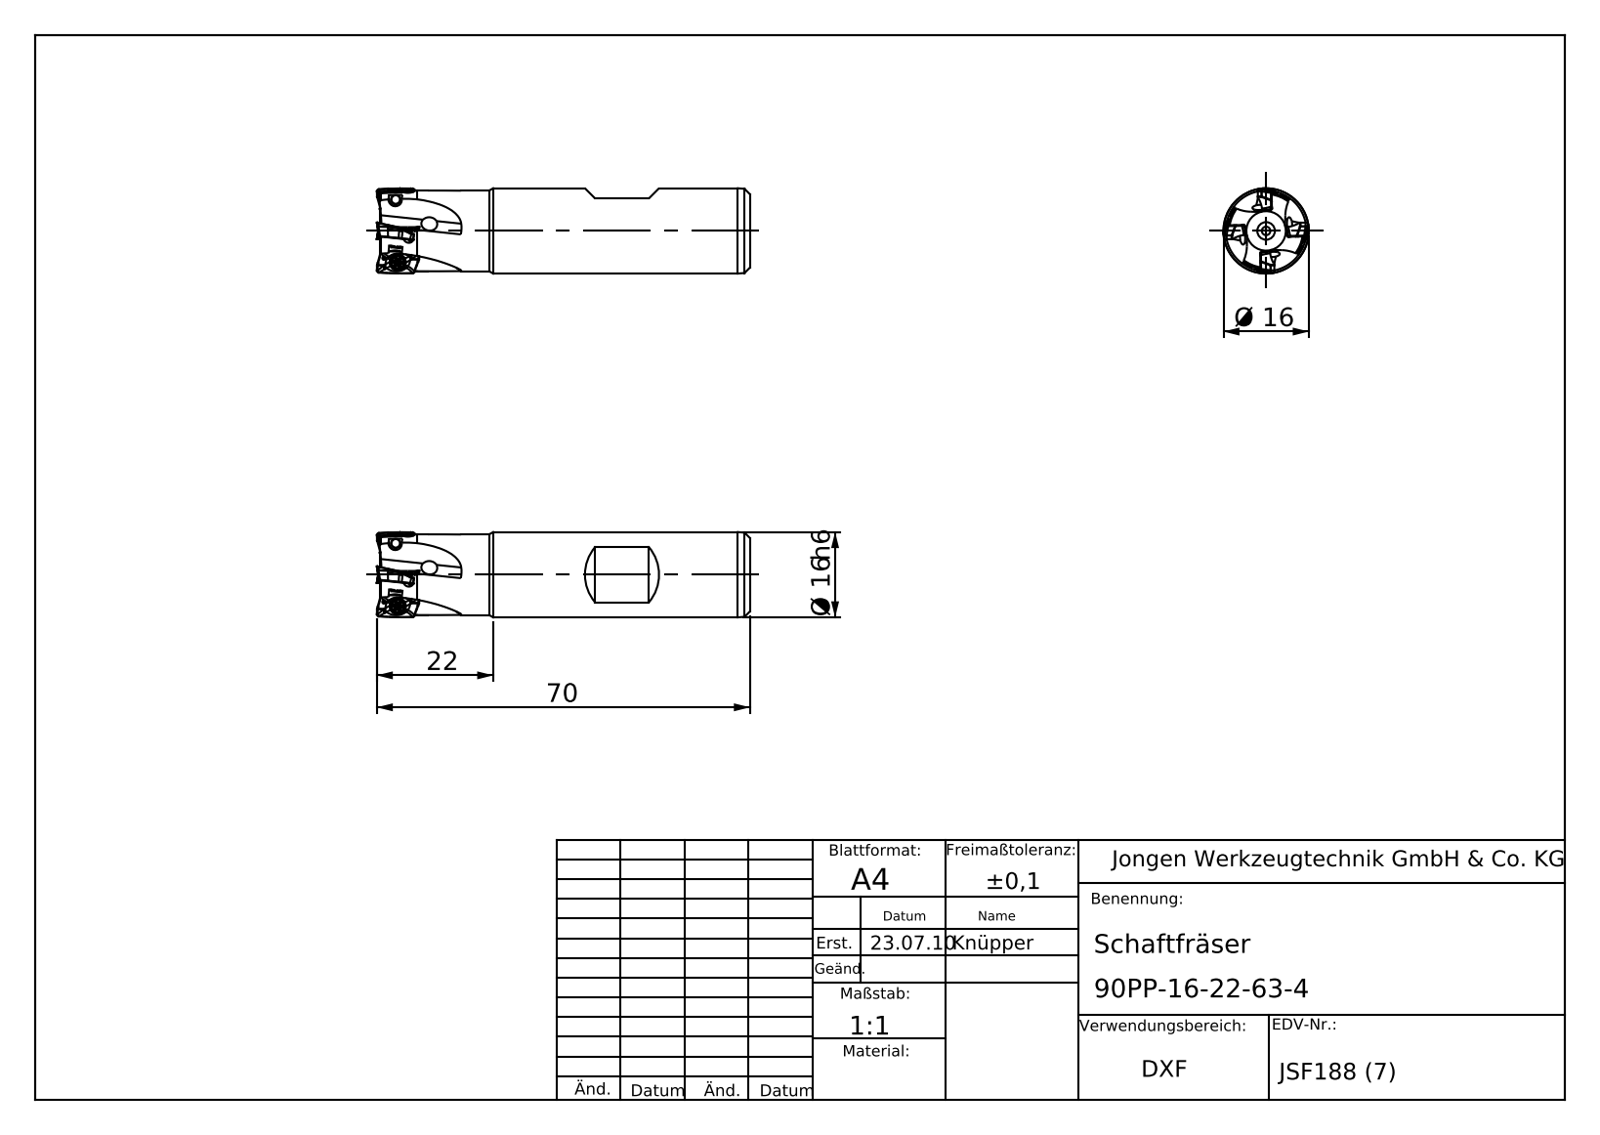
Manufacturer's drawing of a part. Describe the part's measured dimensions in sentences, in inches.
The part is named "90PP-16-22-63-4". Its 3-D file was written by "SolidWorks 2011 (AUTOMOTIVE_DESIGN)". It is 1 solid with 102 faces: 30 planar, 22 cylindrical and 50 other. Overall it measures 2.756 by 0.63 by 0.63 inches. Its volume is 0.751 cubic inches and its surface area 7.876 square inches. Round holes: 4 of diameter 0.098, 1 of diameter 0.063, 1 of diameter 0.157. Round bosses or shafts: 1 of diameter 0.63, 1 of diameter 0.596. Partial cylindrical surfaces (rounded edges, fillets, slot ends): 4 of radius 0.787. The main face-to-face distances are 2.722, 2.736, 0.015.
